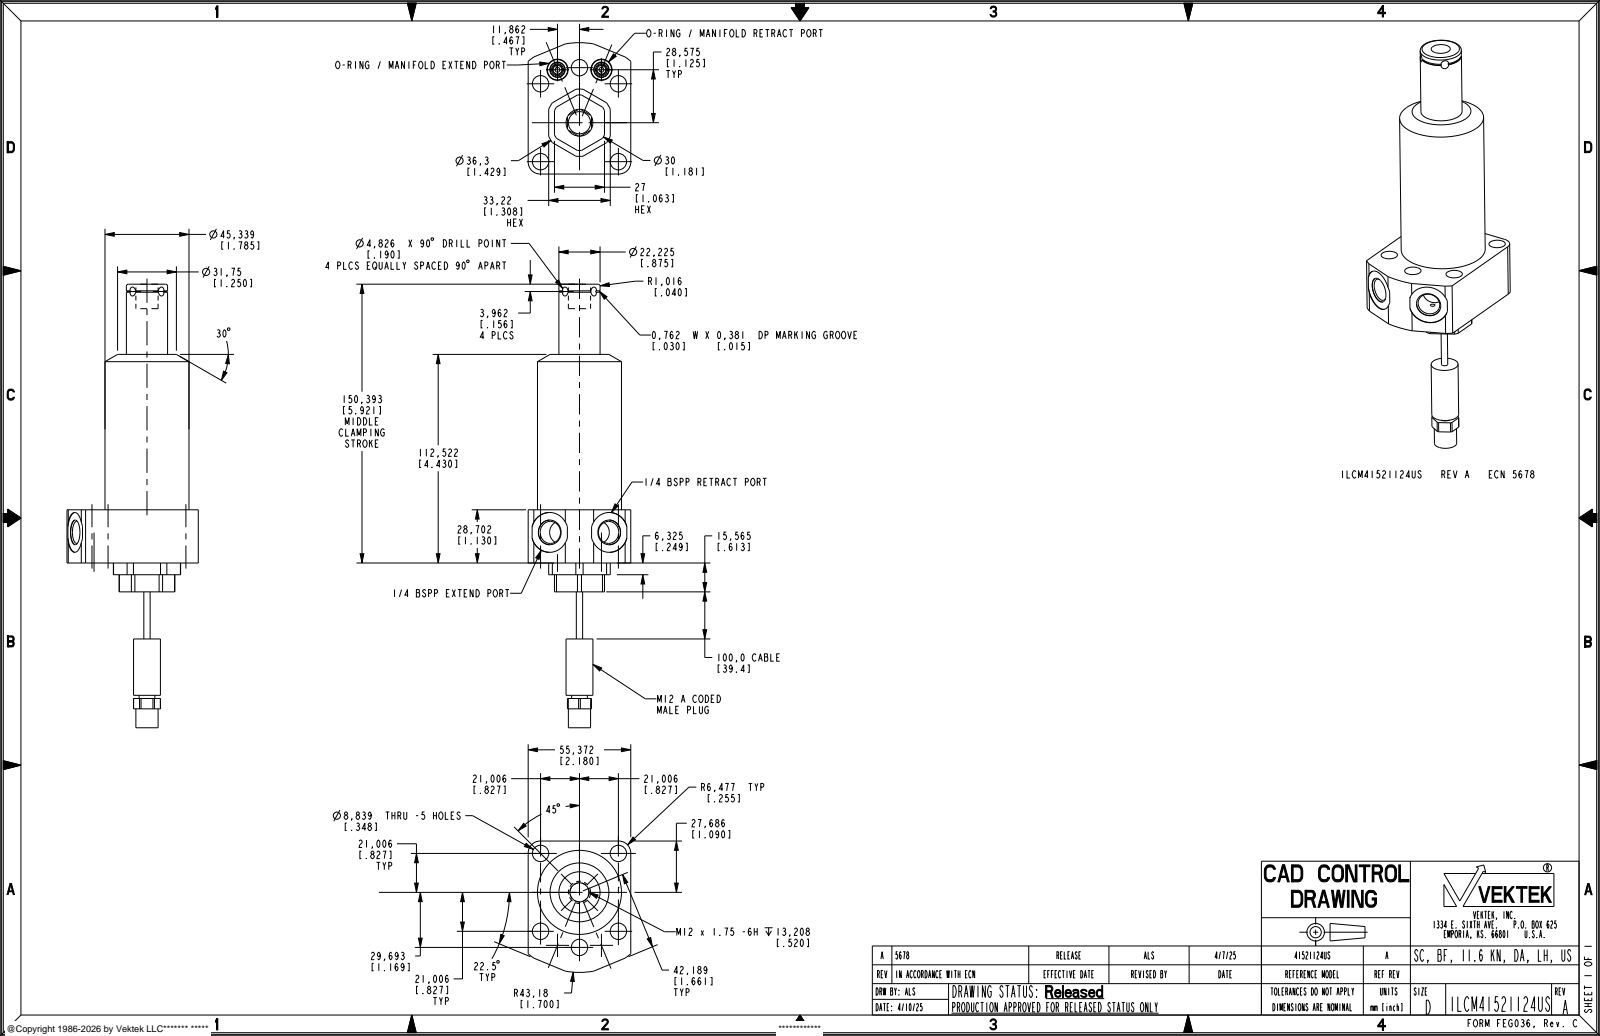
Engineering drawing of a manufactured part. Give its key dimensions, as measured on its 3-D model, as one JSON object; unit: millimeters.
{"part_name": "ILCM41521124US", "step_written_by": "CREO PARAMETRIC BY PTC INC, 2021164 (AUTOMOTIVE_DESIGN)", "units": "millimeters", "bodies": {"solids": 1, "faces": 188, "planar": 75, "cylindrical": 83, "other": 30}, "overall_size": [239.26, 86.87, 63.37], "volume_mm3": 259700, "surface_area_mm2": 38865, "round_holes": [[8.84, 5], [2.49, 2], [6.5, 2], [11.4, 2], [11.89, 2], [13.31, 2], [21.5, 2], [10.31, 1]], "round_bosses_or_shafts": [[5.49, 2], [45.34, 1], [22.23, 1], [14.5, 1], [11.99, 1], [11.99, 1], [8.51, 1], [3.4, 1]], "partial_cylinders_radius": [[6.48, 2], [10.73, 1], [15, 1], [18.15, 1], [43.18, 1]], "face_to_face_distances": [28.7, 55.38, 15.57, 44.27, 3.11, 30.11, 128.09, 112.52, 83.82, 27], "hole_center_spacings": [29.71, 42.02, 11.87, 11.91, 22.73, 30.93, 33.73, 50.42]}
